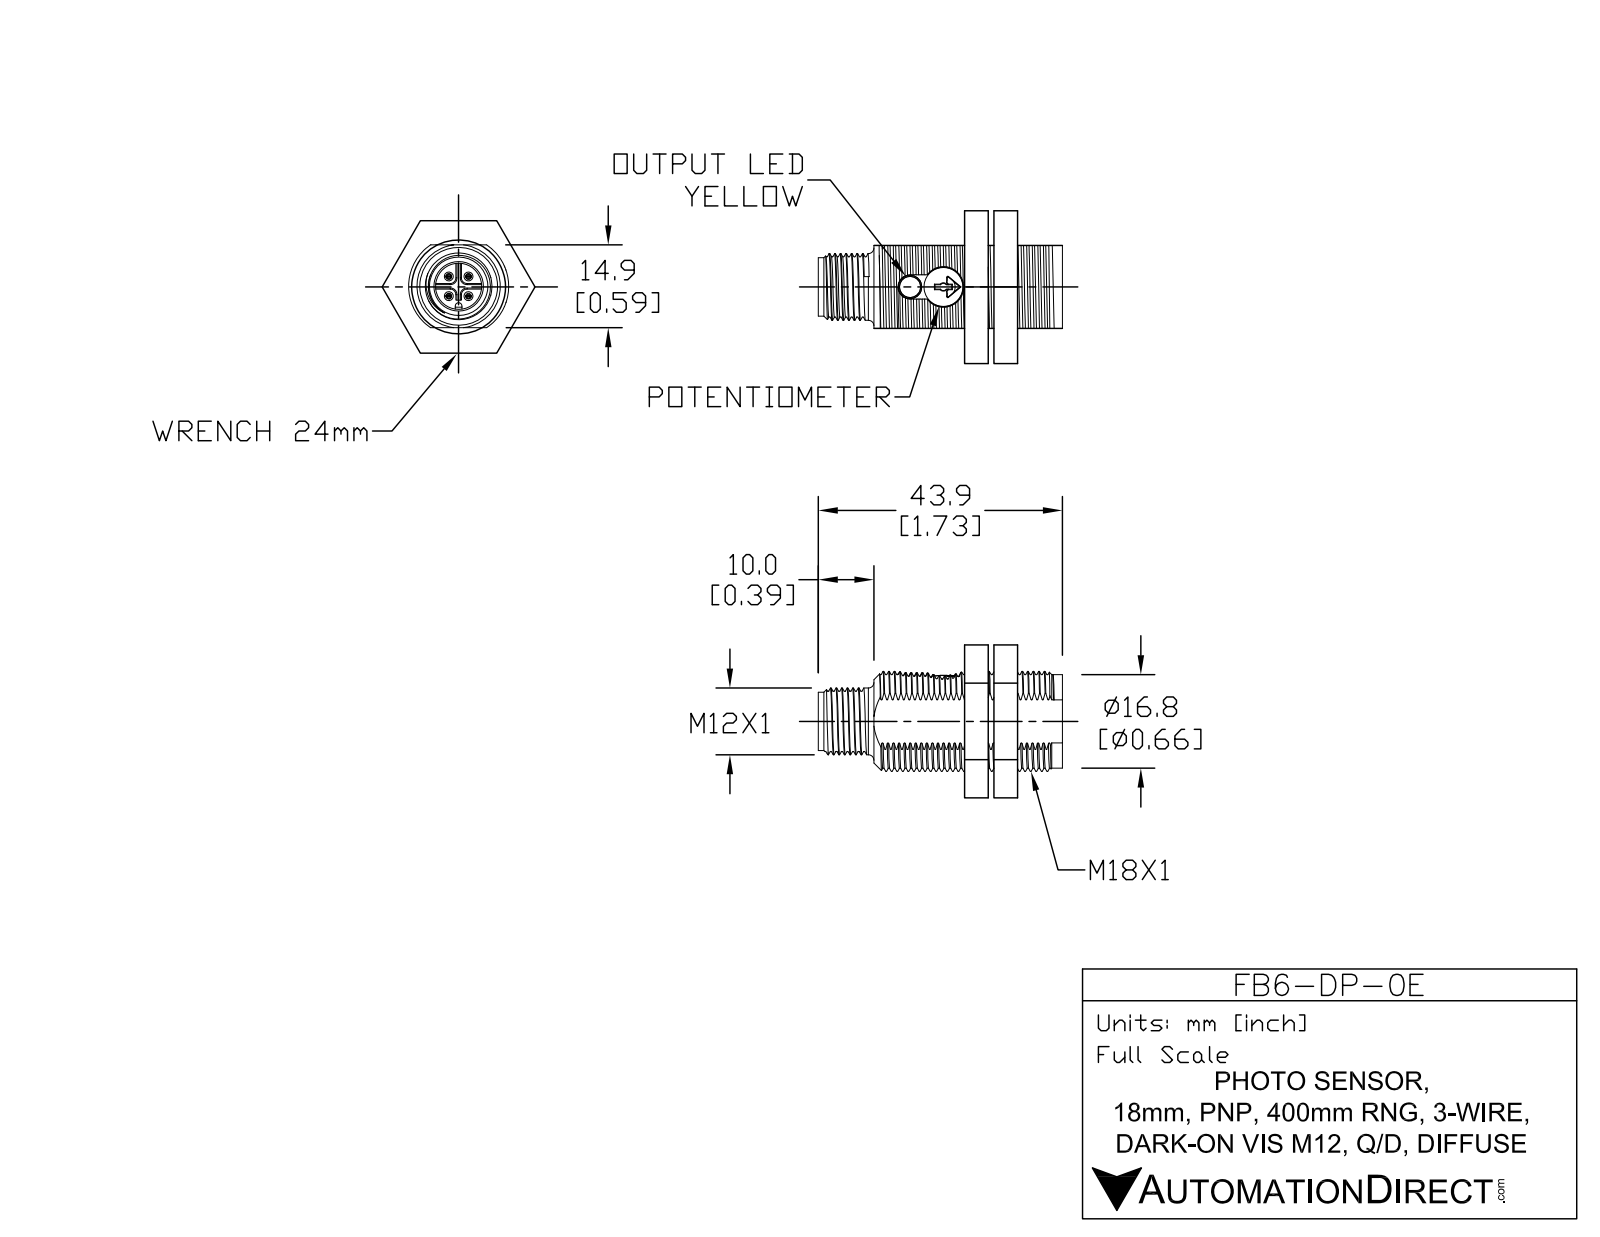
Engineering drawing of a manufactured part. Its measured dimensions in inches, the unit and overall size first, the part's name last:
Units: inches
Overall size (bounding box): 1.728 × 1.09 × 0.967
Round holes (diameter × count): ⌀0.093 ×1, ⌀0.168 ×1, ⌀0.285 ×1, ⌀0.331 ×1
Round bosses / shafts (diameter × count): ⌀0.039 ×4, ⌀0.472 ×1, ⌀0.409 ×1
Partial cylindrical surfaces — rounded edges, fillets, slot ends (radius × count): R0.254 ×2, R0.294 ×2, R0.02 ×1, R0.026 ×1, R0.331 ×1, R0.335 ×1, R0.354 ×1
Main face-to-face distances: 0.315, 0.177, 0.945, 0.591, 0.039, 0.492, 0.138, 0.508, 0.547, 0.193
Hole centre spacings: 0.26
Volume: 0.629 in³ · Surface area: 8.006 in²
Bodies: 7 solids, 237 faces (133 planar, 33 cylindrical, 71 other)
Part name (STEP PRODUCT): FB6-DP-0E
STEP written by: SolidWorks 2011 (AUTOMOTIVE_DESIGN)
